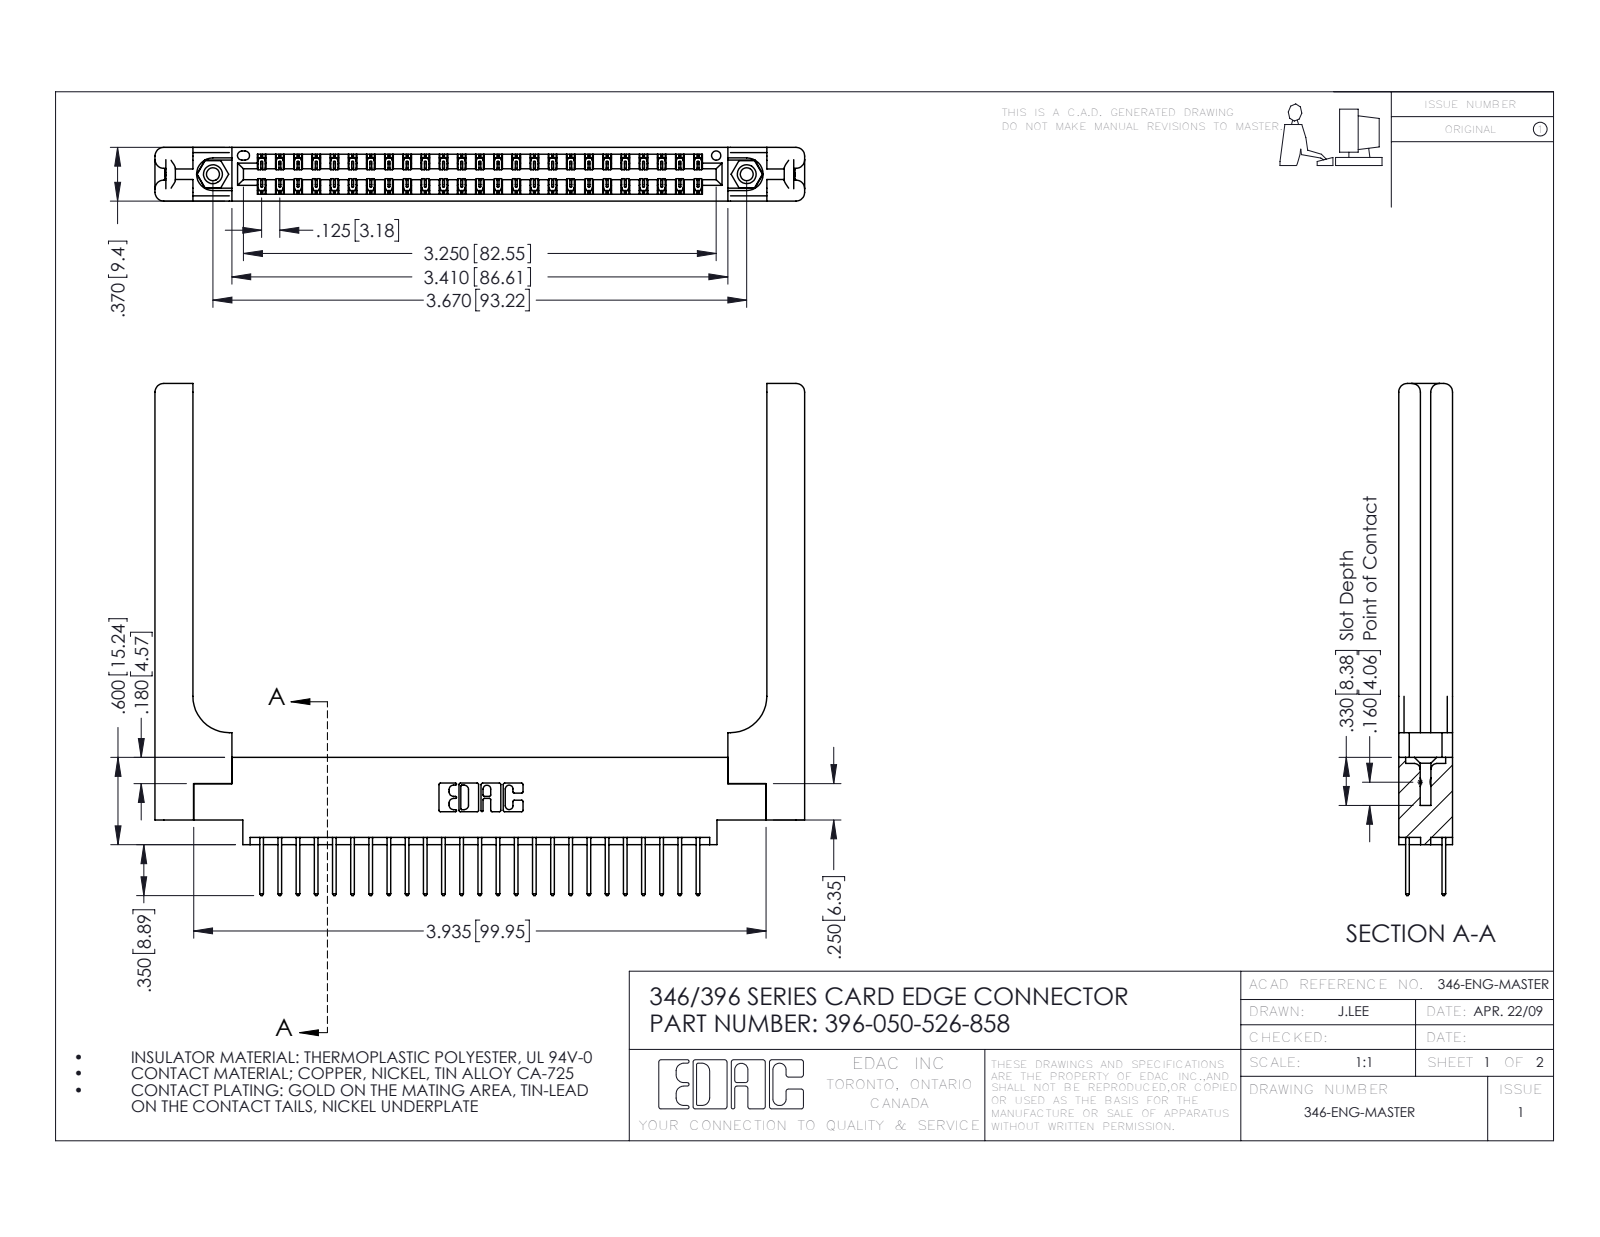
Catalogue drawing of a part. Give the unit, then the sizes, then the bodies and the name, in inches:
Units: inches
Overall size (bounding box): 4.466 × 3.52 × 0.37
Round holes (diameter × count): ⌀0.089 ×2, ⌀0.125 ×2, ⌀0.156 ×2, ⌀0.064 ×1
Round bosses / shafts (diameter × count): ⌀0.155 ×2
Partial cylindrical surfaces — rounded edges, fillets, slot ends (radius × count): R0.006 ×75, R0.01 ×50, R0.01 ×22, R0.06 ×16, R0.007 ×6, R0.031 ×6, R0.026 ×3, R0.014 ×2
Main face-to-face distances: 0.37, 0.072, 0.048, 0.322, 0.148, 0.15, 0.25, 0.025, 0.298, 0.275
Hole centre spacings: 0.246, 3.462, 3.67
Volume: 1.12 in³ · Surface area: 31.27 in²
Bodies: 55 solids, 2982 faces (1978 planar, 944 cylindrical, 60 other)
Part name (STEP PRODUCT): 396-050-526-858; 346 Part_0.170 Offset - 0.156 Dia-TH; 345-250-001_345-250-001-102; 346-220-058_345-220-058 (+1 more)
STEP written by: SolidWorks 2016 (CONFIG_CONTROL_DESIGN)
